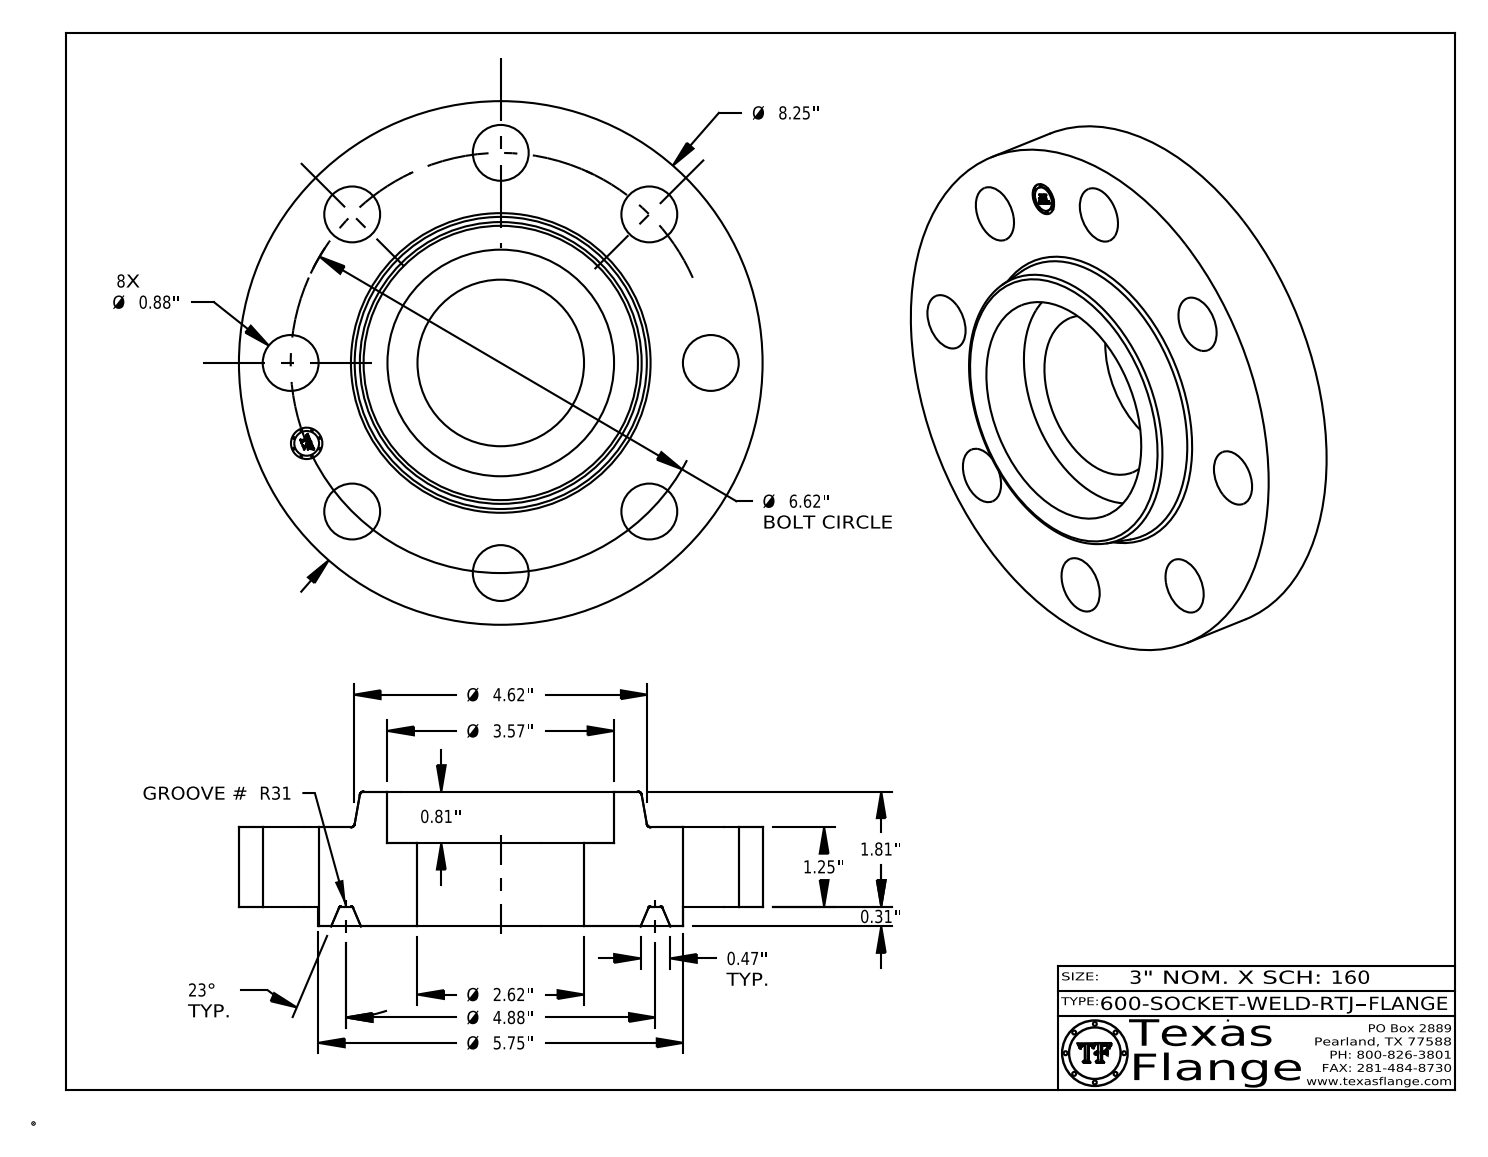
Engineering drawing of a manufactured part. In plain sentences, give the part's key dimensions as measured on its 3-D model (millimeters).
The part is named "600-SOCKET-WELD-RTJ". Its 3-D file was written by "CATIA V5 STEP AP214 (AUTOMOTIVE_DESIGN)". It is 1 solid with 438 faces: 372 planar, 52 cylindrical and 14 other. Overall it measures 209.6 by 209.6 by 53.9 millimeters. Its volume is 1 000 000 cubic millimeters and its surface area 119 000 square millimeters. Round holes: 8 of diameter 22.4, 1 of diameter 12.6, 1 of diameter 66.6, 1 of diameter 90.7. Round bosses or shafts: 8 of diameter 0.8, 1 of diameter 209.6, 1 of diameter 146.1, 1 of diameter 9.9. The main face-to-face distances are 31.8, 8, 39.7, 53.9, 46, 14.2, 33.4, 25.4, 6.4, 20.6. The hole center spacings are 84.1, 64.3, 155.3, 118.9, 118.9, 32.8, 93.4, 164.9.
